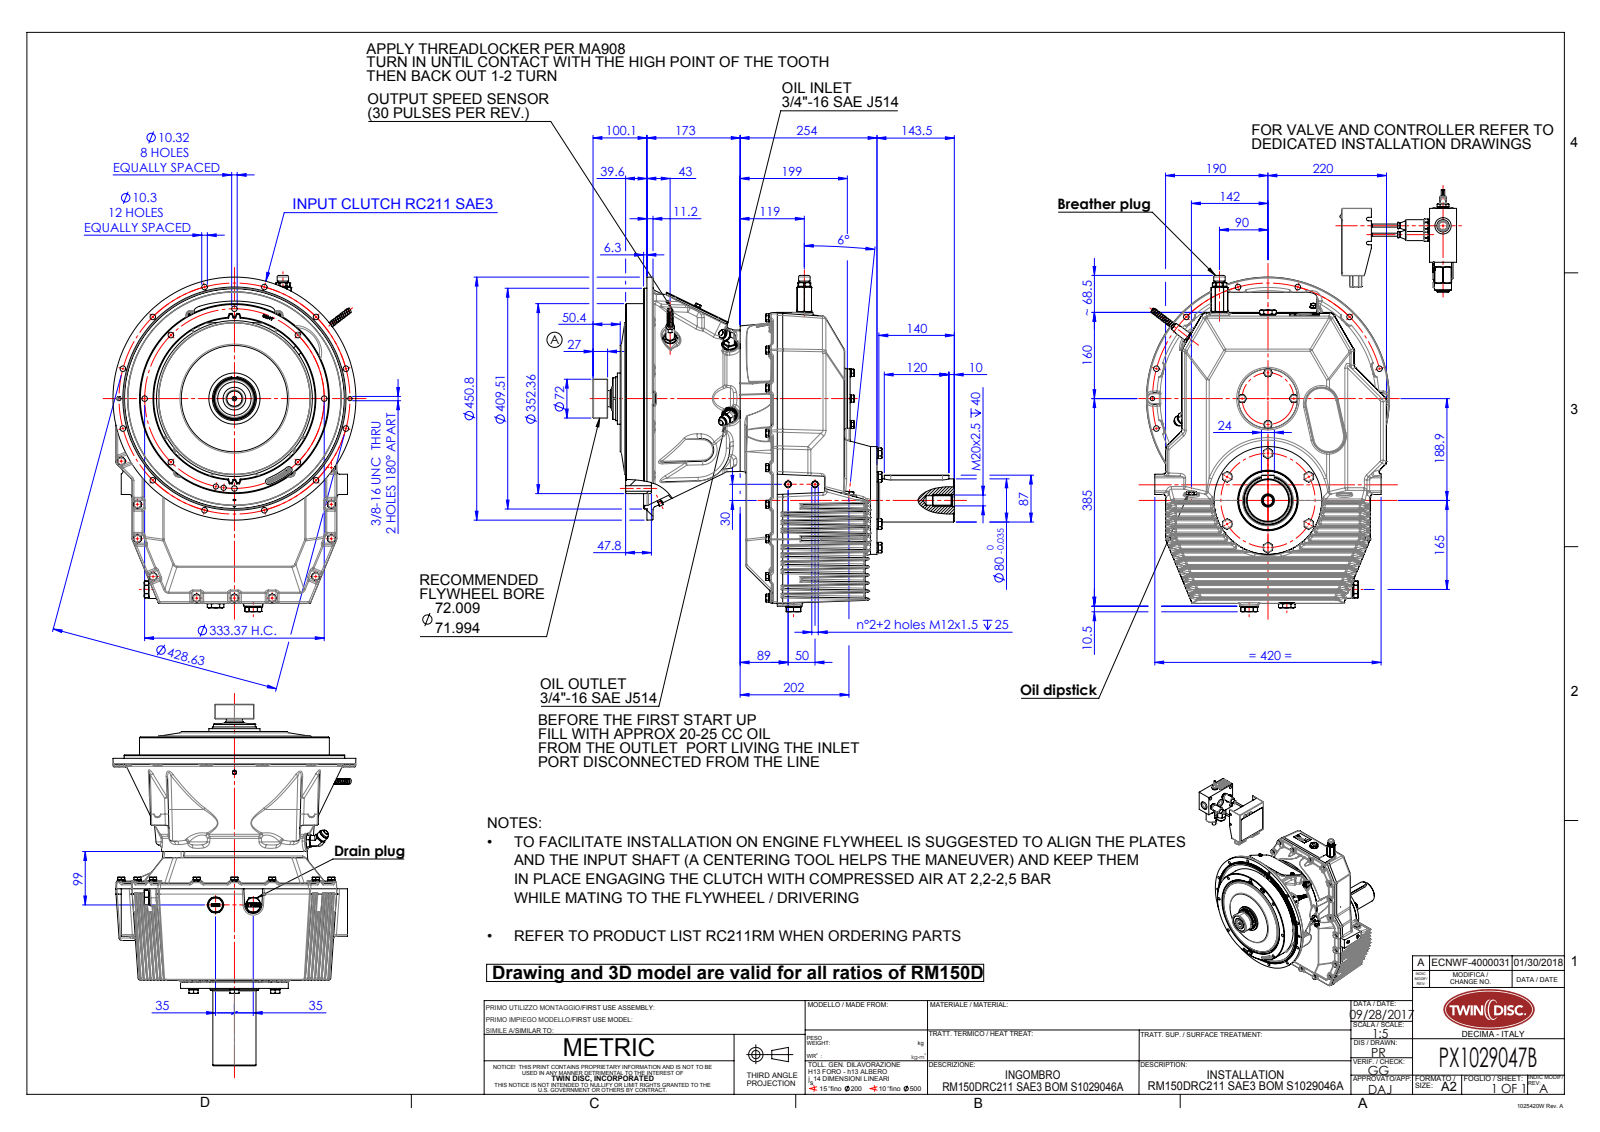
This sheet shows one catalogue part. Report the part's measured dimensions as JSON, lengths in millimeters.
{"part_name": "ITrm150-002-installation; ITrm150-017-installation; ITrm120-003_rev00-installation; IT4588002_rev00-installation (+4 more)", "step_written_by": "SolidWorks 2015 (AUTOMOTIVE_DESIGN)", "units": "millimeters", "bodies": {"solids": 49, "faces": 7488, "planar": 2687, "cylindrical": 1867, "other": 2934}, "overall_size": [782.95, 670.6, 575.42], "volume_mm3": 10280000, "surface_area_mm2": 2734000, "round_holes": [[8.5, 36], [6.8, 25], [8.2, 21], [4.37, 13], [10.2, 13], [10.3, 12], [30, 10], [10, 9], [11, 9], [4.37, 8], [10.32, 8], [12, 8]], "round_bosses_or_shafts": [[8, 26], [14.8, 25], [12.2, 25], [10, 10], [18.1, 6], [16.2, 6], [22.86, 4], [16.74, 4]], "partial_cylinders_radius": [[0.1, 224], [3, 173], [2, 135], [2.5, 74], [5, 49], [6.5, 43], [8, 41], [1.5, 35]], "face_to_face_distances": [10, 217.24, 11, 206.24, 135, 60, 173, 3.05, 41.39, 232], "hole_center_spacings": [12.7, 15.37, 28.07, 57.4, 87.5, 138.58, 151.56, 51.37]}
